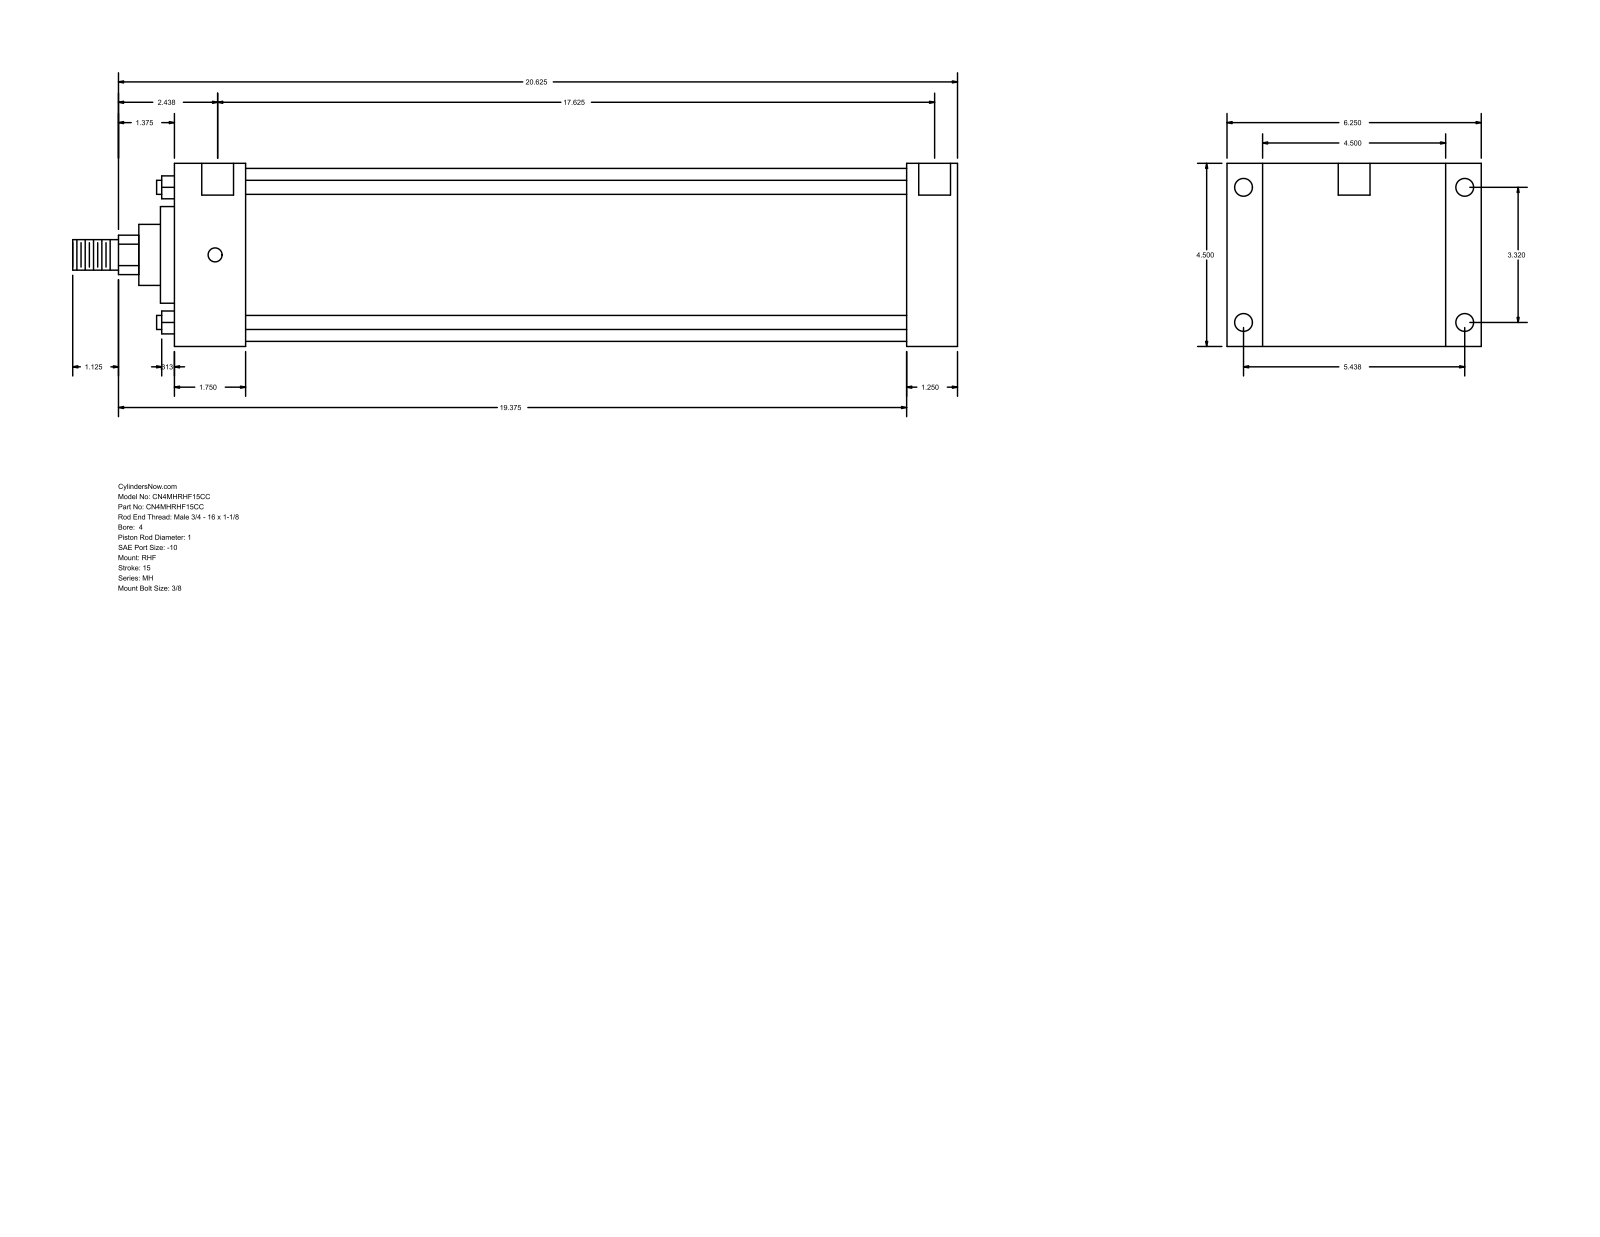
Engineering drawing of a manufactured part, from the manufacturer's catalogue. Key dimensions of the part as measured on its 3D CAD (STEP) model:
Part name (STEP PRODUCT): MH_RHF__0400_1
STEP written by: GSSL Pune (CONFIG_CONTROL_DESIGN)
Units: millimetres
Bodies: 0 solids, 90 faces (61 planar, 29 cylindrical, 0 other)
Overall size (bounding box): 552.45 × 158.75 × 114.3
Round holes (diameter × count): ⌀8.73 ×4, ⌀11.13 ×4, ⌀19.84 ×2
Round bosses / shafts (diameter × count): ⌀8.76 ×4, ⌀107.95 ×1, ⌀60.33 ×1, ⌀38.1 ×1, ⌀25.4 ×1, ⌀19.05 ×1
Partial cylindrical surfaces — rounded edges, fillets, slot ends (radius × count): R12.29 ×1
Main face-to-face distances: 114.3, 488.96, 457.2, 31.76, 22.23, 136.53, 44.46, 412.74, 444.5, 158.76
Hole centre spacings: 84.32, 138.12, 161.82, 450.85, 1.58, 1.59, 447.68, 449.26
